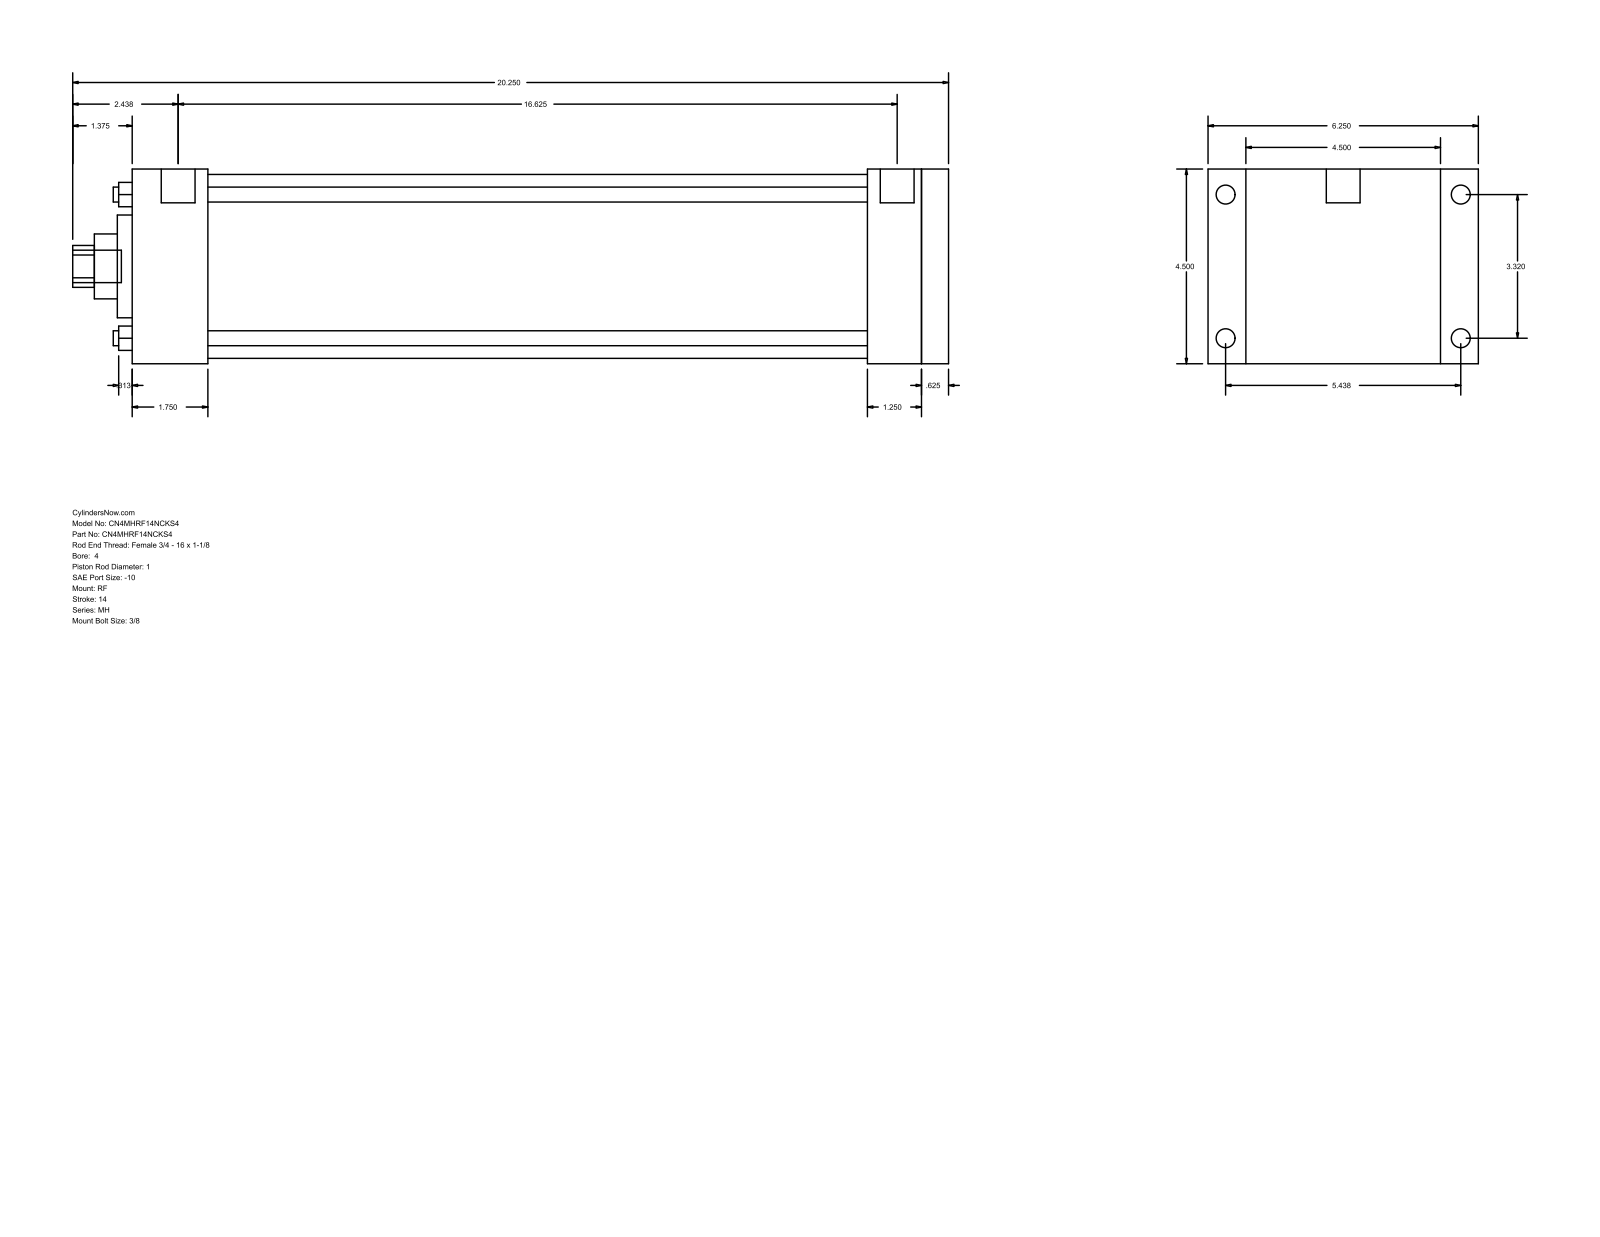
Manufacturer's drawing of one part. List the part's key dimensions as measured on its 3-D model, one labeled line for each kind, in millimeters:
Part name (STEP PRODUCT): MH_RF__0400_1
STEP written by: GSSL Pune (CONFIG_CONTROL_DESIGN)
Units: millimetres
Bodies: 0 solids, 94 faces (65 planar, 29 cylindrical, 0 other)
Overall size (bounding box): 514.35 × 158.75 × 114.3
Round holes (diameter × count): ⌀8.76 ×4, ⌀25.4 ×1, ⌀38.1 ×1, ⌀60.33 ×1, ⌀107.95 ×1
Round bosses / shafts (diameter × count): ⌀11.13 ×4, ⌀8.73 ×4, ⌀19.84 ×2, ⌀19.05 ×1
Partial cylindrical surfaces — rounded edges, fillets, slot ends (radius × count): R12.29 ×1
Main face-to-face distances: 114.3, 479.43, 15.87, 463.56, 44.46, 419.1, 434.97, 431.81, 387.35, 31.75
Hole centre spacings: 59.62, 84.32, 119.25
